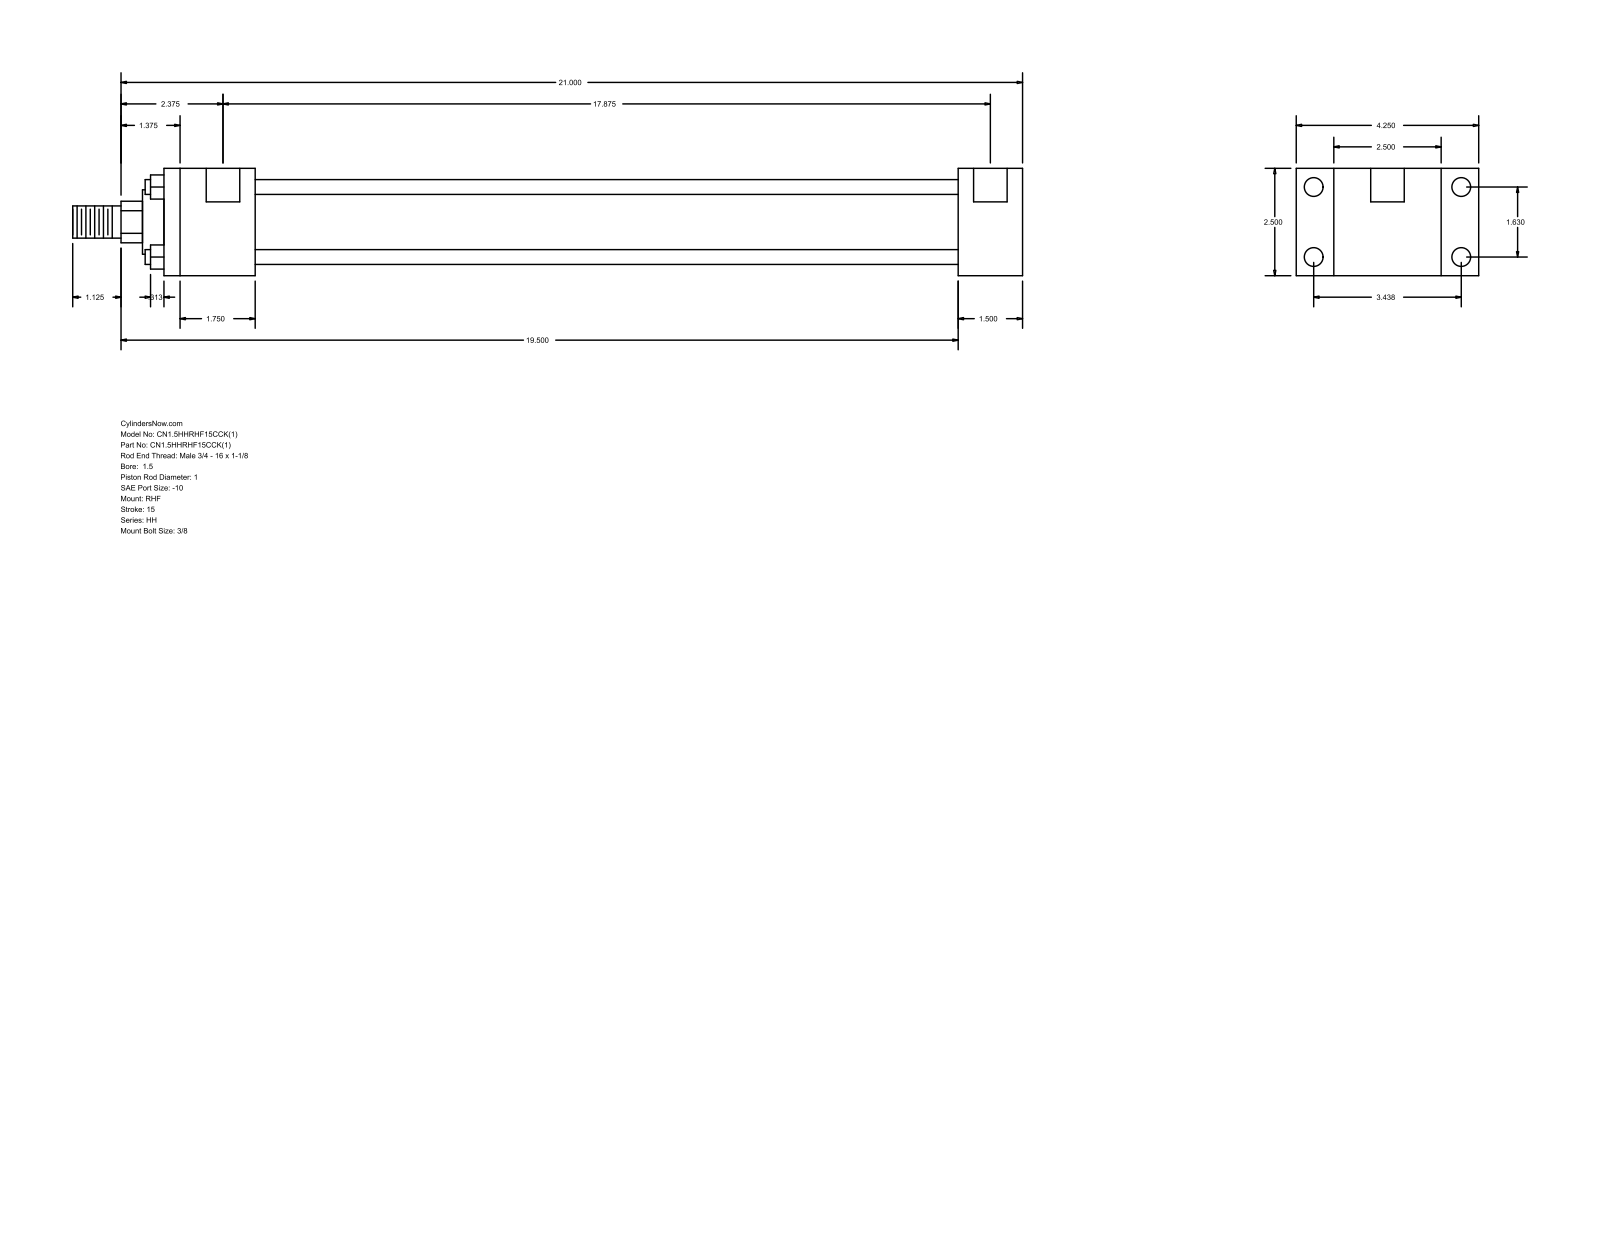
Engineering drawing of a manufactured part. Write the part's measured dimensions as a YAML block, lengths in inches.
part_name: "HH_RHF__0150_1"
step_written_by: "GSSL Pune (CONFIG_CONTROL_DESIGN)"
units: inches
bodies: {solids: 0, faces: 88, planar: 60, cylindrical: 28, other: 0}
overall_size: [22.125, 4.25, 2.5]
round_holes:
  - {diameter: 0.219, count: 4}
  - {diameter: 0.438, count: 4}
  - {diameter: 0.781, count: 2}
round_bosses_or_shafts:
  - {diameter: 0.345, count: 4}
  - {diameter: 1.75, count: 1}
  - {diameter: 1.5, count: 1}
  - {diameter: 1, count: 1}
  - {diameter: 0.75, count: 1}
partial_cylinders:
  - {radius: 0.484, count: 1}
face_to_face_distances: [2.5, 0.875, 3.375, 1.5, 4.25, 16.375, 17.875, 2.125, 18.5, 20]
hole_center_spacings: [0.063, 1.63, 3.438, 3.805, 17.937, 18, 17.875]
